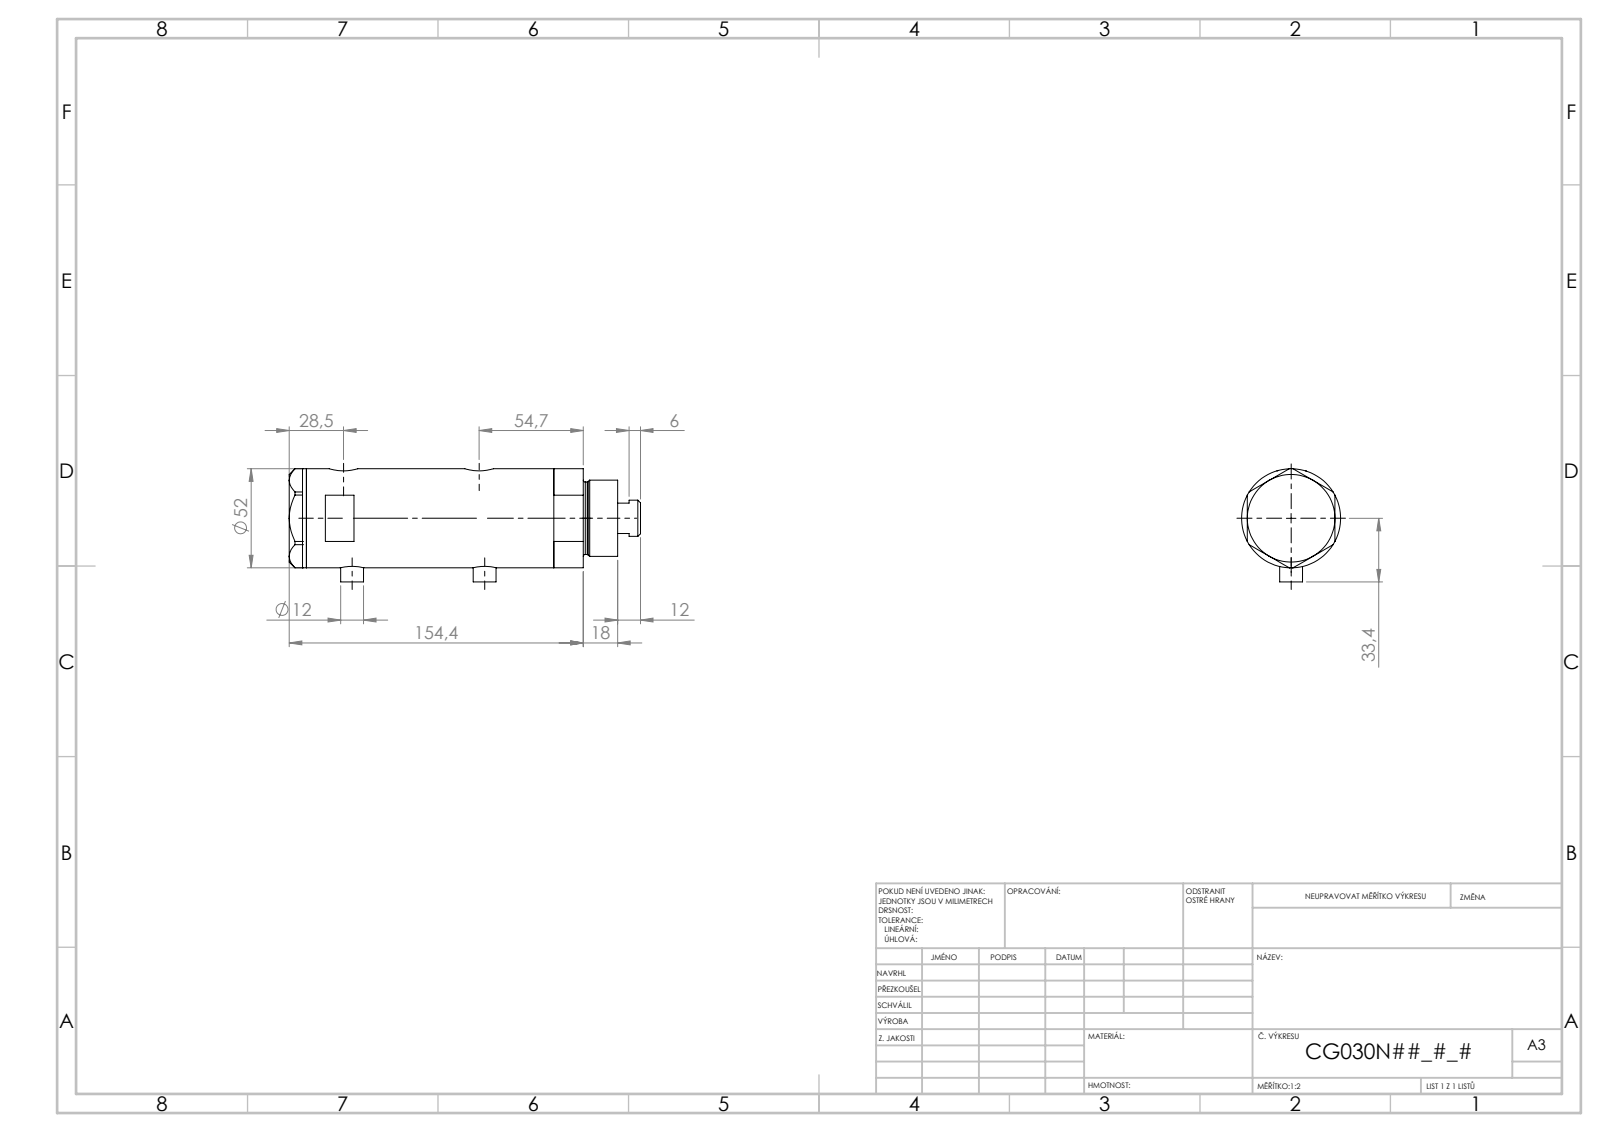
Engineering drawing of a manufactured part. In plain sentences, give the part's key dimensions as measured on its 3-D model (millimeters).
The part is named "V270CG_VC; V270CG_BACK; V270CG_FRONT; V270CG_MIDDLE". Its 3-D file was written by "SolidWorks 2019 (CONFIG_CONTROL_DESIGN)". It is 4 solids with 140 faces: 67 planar, 53 cylindrical and 20 other. Overall it measures 184.4 by 53.1 by 52 millimeters. Its volume is 329 941 cubic millimeters and its surface area 76 850 square millimeters. Round holes: 2 of diameter 5, 2 of diameter 9.64, 2 of diameter 12.5, 2 of diameter 15, 1 of diameter 6.5, 1 of diameter 20, 1 of diameter 21.5, 1 of diameter 30, 1 of diameter 33, 1 of diameter 44. Round bosses or shafts: 2 of diameter 12, 1 of diameter 52, 1 of diameter 40, 1 of diameter 38, 1 of diameter 19. The main face-to-face distances are 93.5, 23.8, 69.7, 9, 32.8, 102.5, 46, 138.9, 129.9, 106.1. The hole center spacings are 2.9, 4.5, 66.7, 69.6, 71.2, 74.1.
